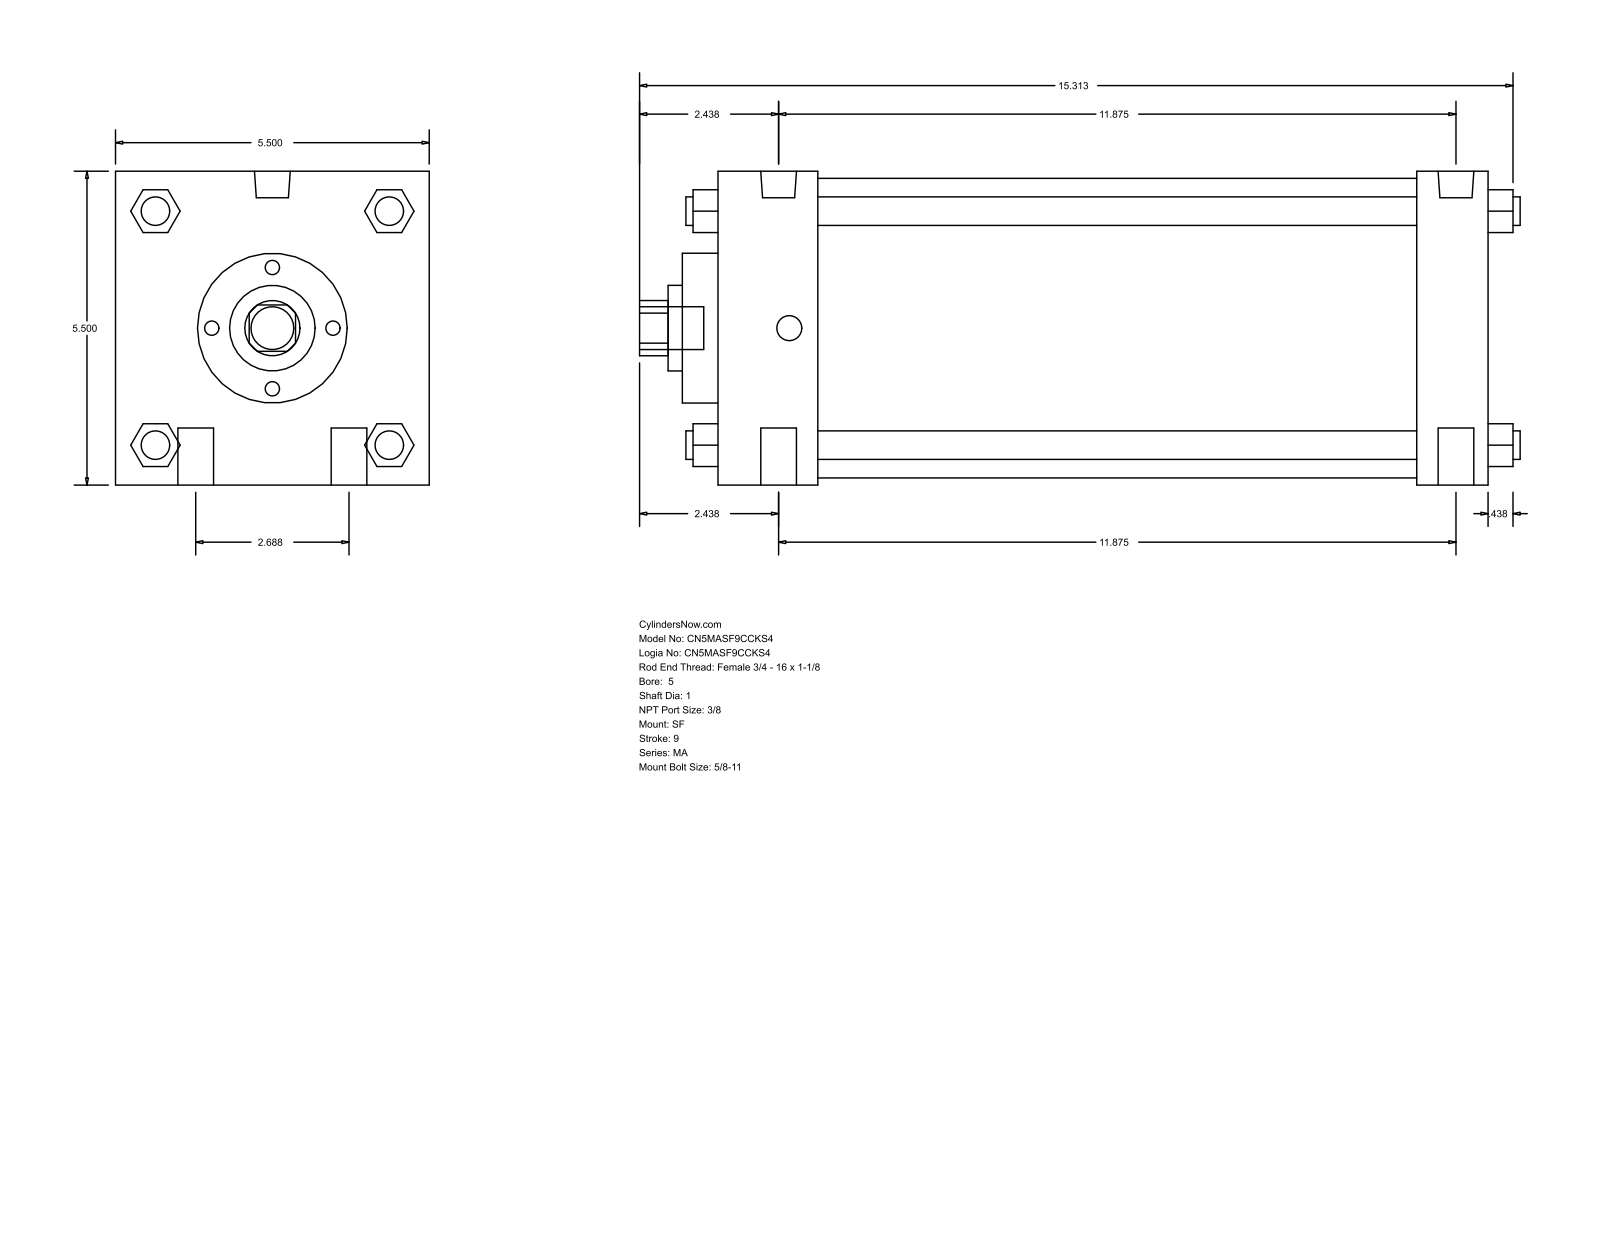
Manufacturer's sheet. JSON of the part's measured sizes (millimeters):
{"part_name": "MA_SF__0500_1", "step_written_by": "GSSL Pune (CONFIG_CONTROL_DESIGN)", "units": "millimeters", "bodies": {"solids": 0, "faces": 126, "planar": 95, "cylindrical": 31, "other": 0}, "overall_size": [392.11, 139.7, 139.7], "round_holes": [[25.4, 1], [38.1, 1], [66.67, 1], [133.35, 1]], "round_bosses_or_shafts": [[15.88, 4], [12.7, 4], [15.93, 2], [11.11, 2], [19.05, 1]], "partial_cylinders_radius": [[12.29, 1]], "face_to_face_distances": [139.7, 342.9, 44.46, 311.15, 266.69, 298.44, 31.75, 15.87, 60.33, 327.02]}
